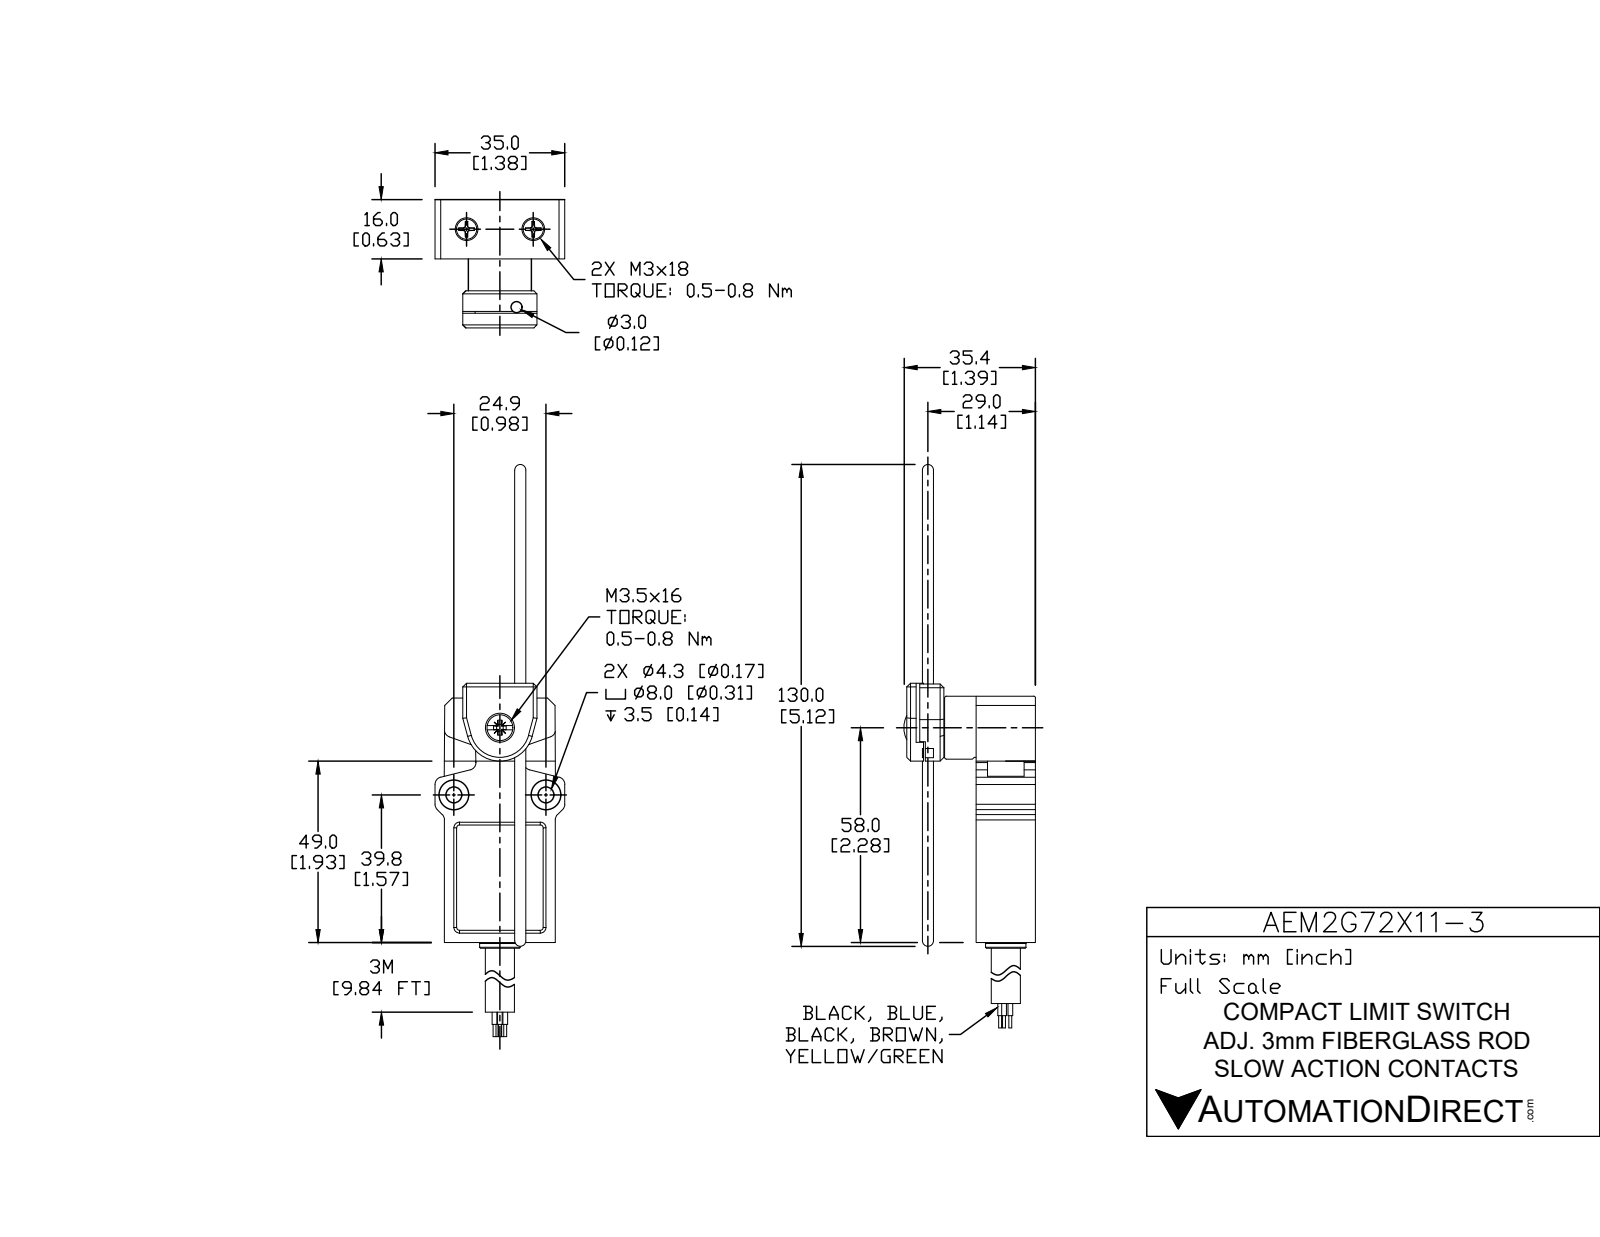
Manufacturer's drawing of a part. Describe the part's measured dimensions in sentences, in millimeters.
The part is named "AEM2G72X11-3". Its 3-D file was written by "SolidWorks 2017 (AUTOMOTIVE_DESIGN)". It is 4 solids with 187 faces: 121 planar, 57 cylindrical and 9 other. Overall it measures 137.8 by 35.1 by 35 millimeters. Its volume is 36 590 cubic millimeters and its surface area 13 280 square millimeters. Round holes: 2 of diameter 4.4, 2 of diameter 8.2, 1 of diameter 3, 1 of diameter 8, 1 of diameter 11. Round bosses or shafts: 1 of diameter 17, 1 of diameter 8, 1 of diameter 7. Partial cylindrical surfaces (rounded edges, fillets, slot ends): 12 of radius 2, 2 of radius 9, 1 of radius 4.6, 1 of radius 6.4, 1 of radius 6.5. The main face-to-face distances are 16, 30, 24.5, 8.5, 49, 3, 17, 66, 18.3, 4. The hole center spacings are 21.7, 21.9, 25.
